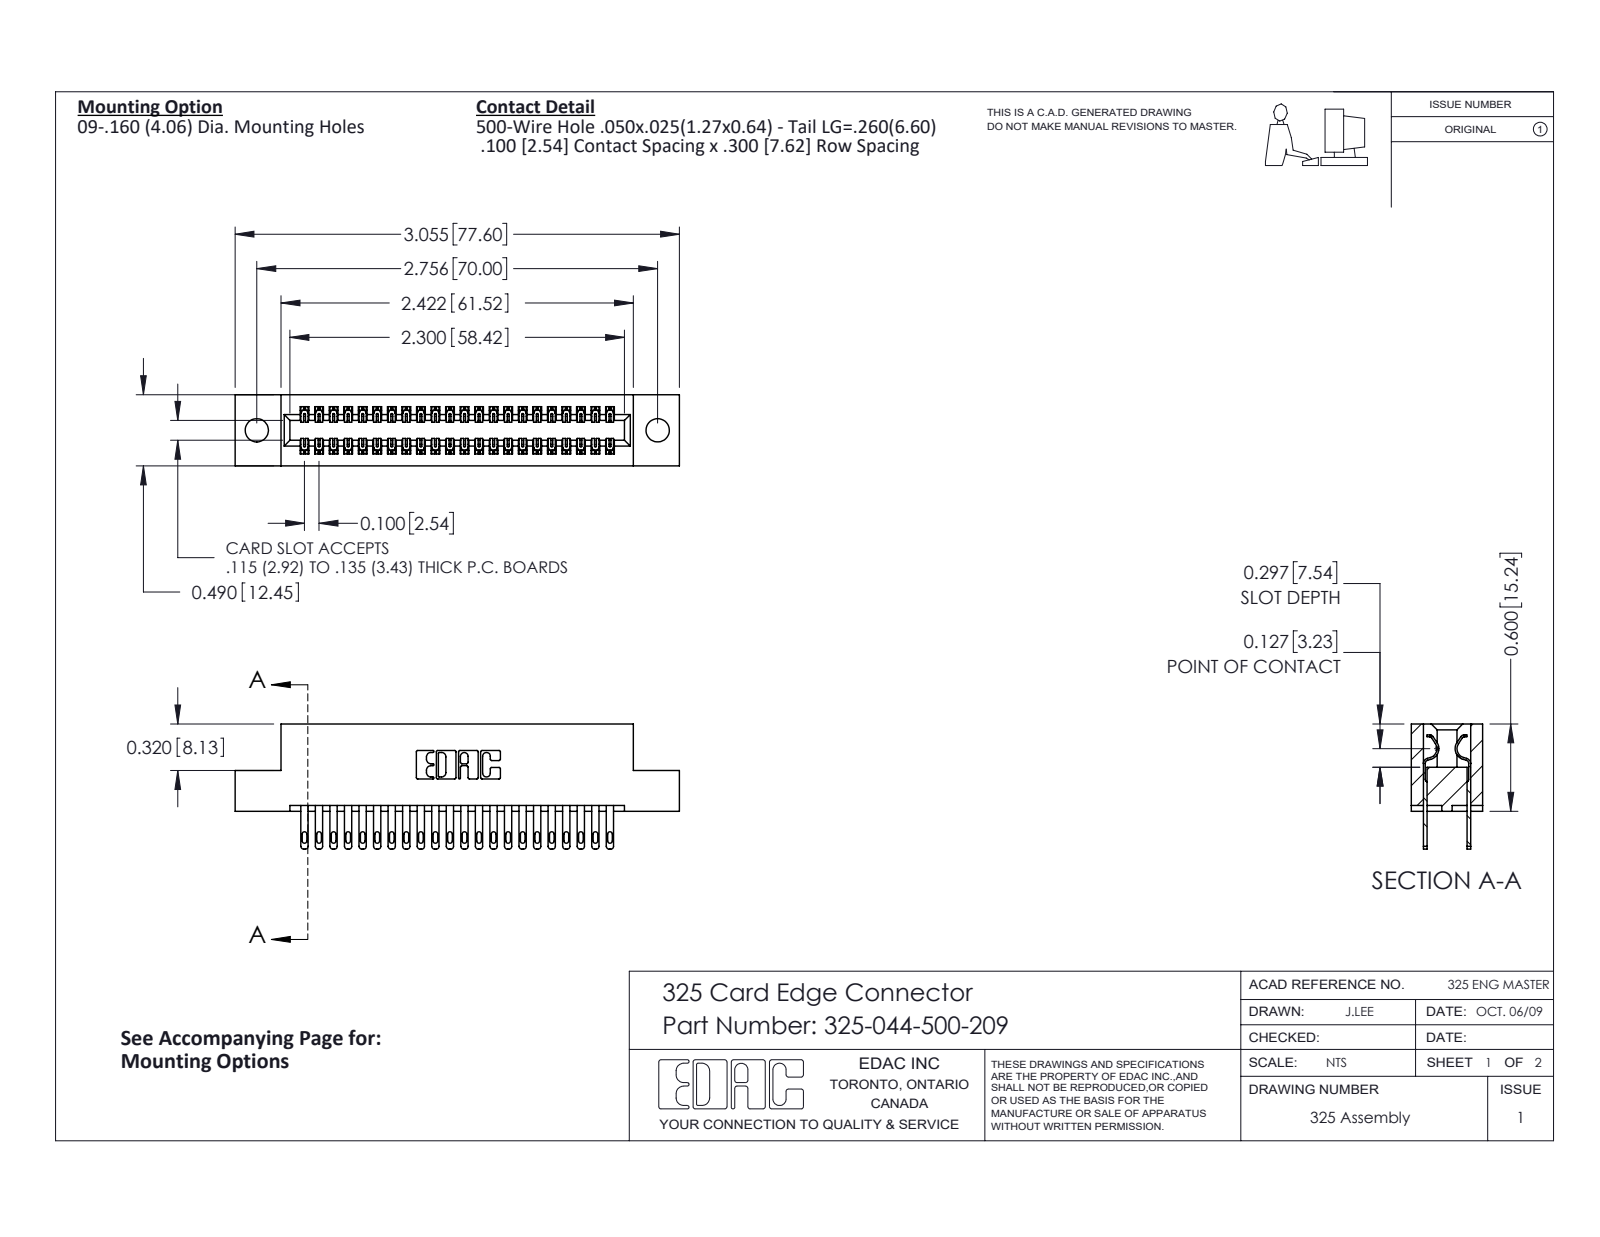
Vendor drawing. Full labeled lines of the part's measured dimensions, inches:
Part name (STEP PRODUCT): 325 Part_.160 TH; 325-292-001_325-293-100; 325-044-500-209
STEP written by: SolidWorks 2016 (CONFIG_CONTROL_DESIGN)
Units: inches
Bodies: 45 solids, 2226 faces (1390 planar, 836 cylindrical, 0 other)
Overall size (bounding box): 3.055 × 0.86 × 0.49
Volume: 0.594 in³ · Surface area: 18.13 in²
Round holes (diameter × count): ⌀0.16 ×2
Partial cylindrical surfaces — rounded edges, fillets, slot ends (radius × count): R0.006 ×66, R0.016 ×44, R0.02 ×44, R0.01 ×22, R0.007 ×6, R0.031 ×6, R0.026 ×3, R0.014 ×2
Main face-to-face distances: 0.083, 0.407, 0.3, 0.107, 0.383, 0.025, 0.49, 0.325, 0.04, 0.275
Hole centre spacings: 2.756
